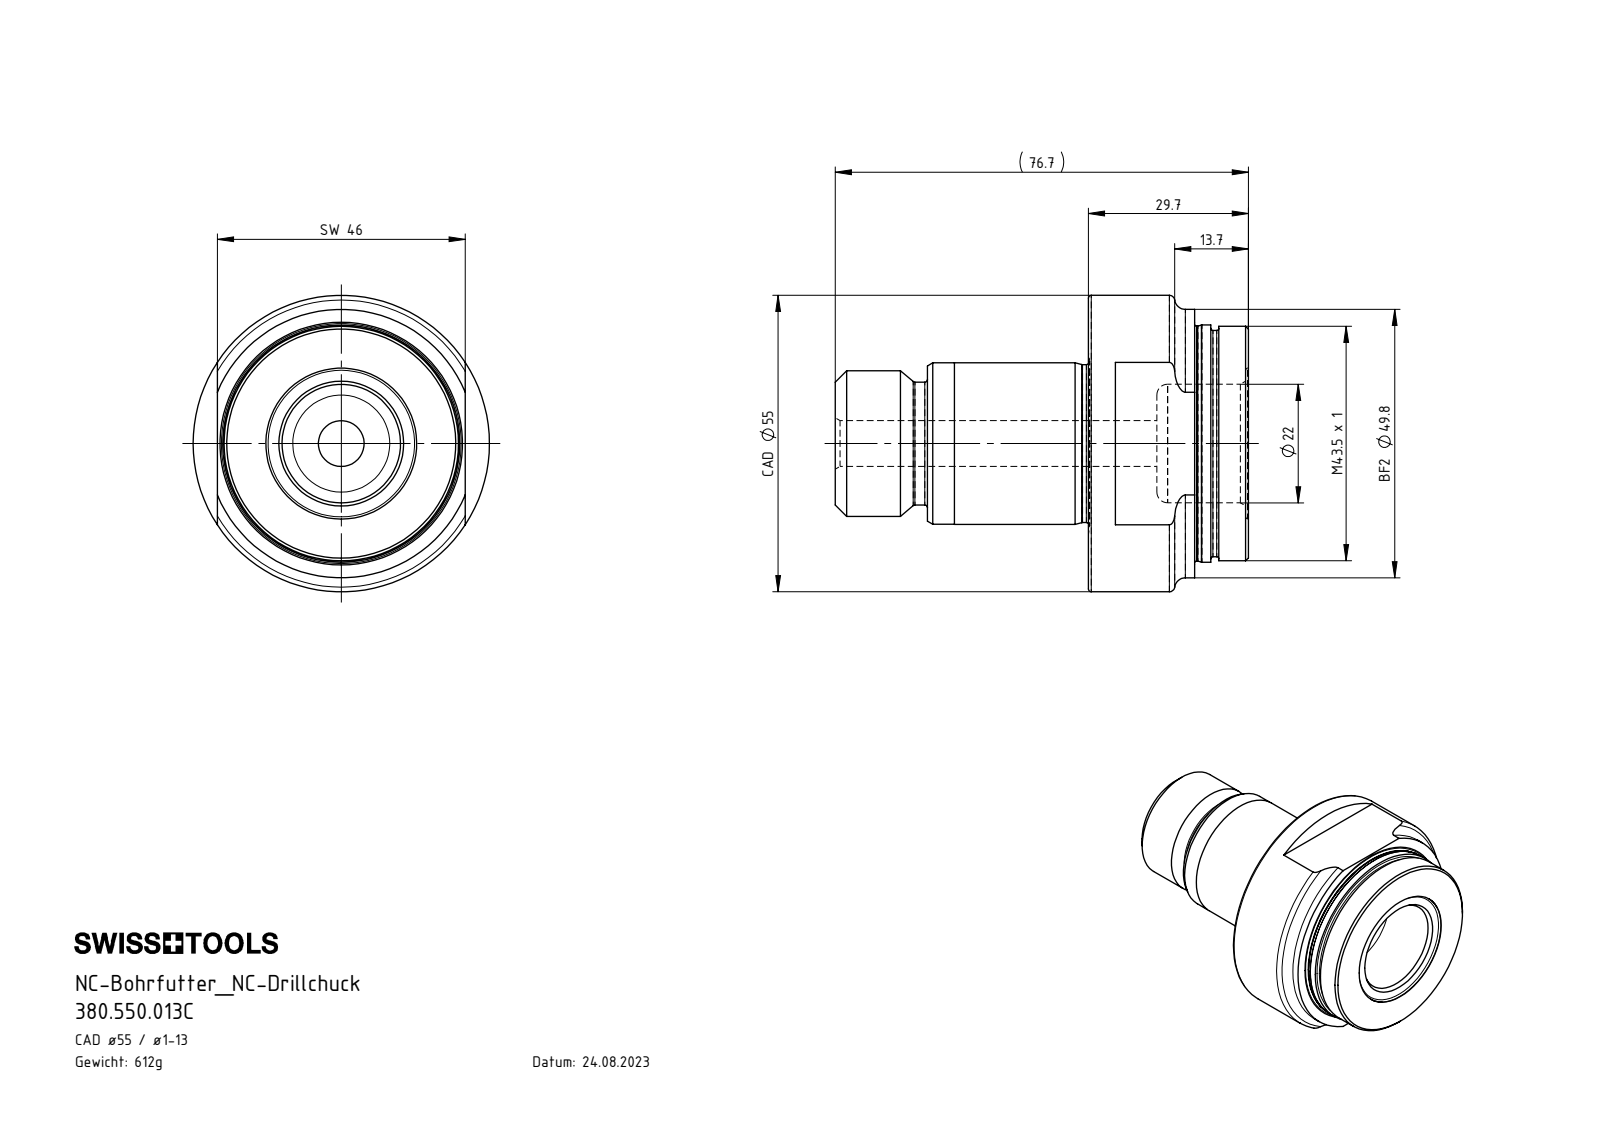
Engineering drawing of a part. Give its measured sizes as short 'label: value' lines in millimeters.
name: CA5-BF1.K01.090_A; 380.550.013C
written by: SolidWorks 2022 (CONFIG_CONTROL_DESIGN)
unit: mm
bodies: 1 solid, 93 faces (14 planar, 29 cylindrical, 50 other)
size: 76.67 × 55 × 55
volume: 77 901 mm³; area: 16 220 mm²
holes: 1× ⌀8.5, 1× ⌀22, 1× ⌀28
bosses: 1× ⌀55, 1× ⌀44, 1× ⌀43.6, 1× ⌀43.5, 1× ⌀42, 1× ⌀30, 1× ⌀29.95, 1× ⌀29.3
rounds: 1× R24.9
face distances: 29.67, 46, 47, 76.67, 66.7, 19.7, 9.97, 29.9, 17.1, 49.6
